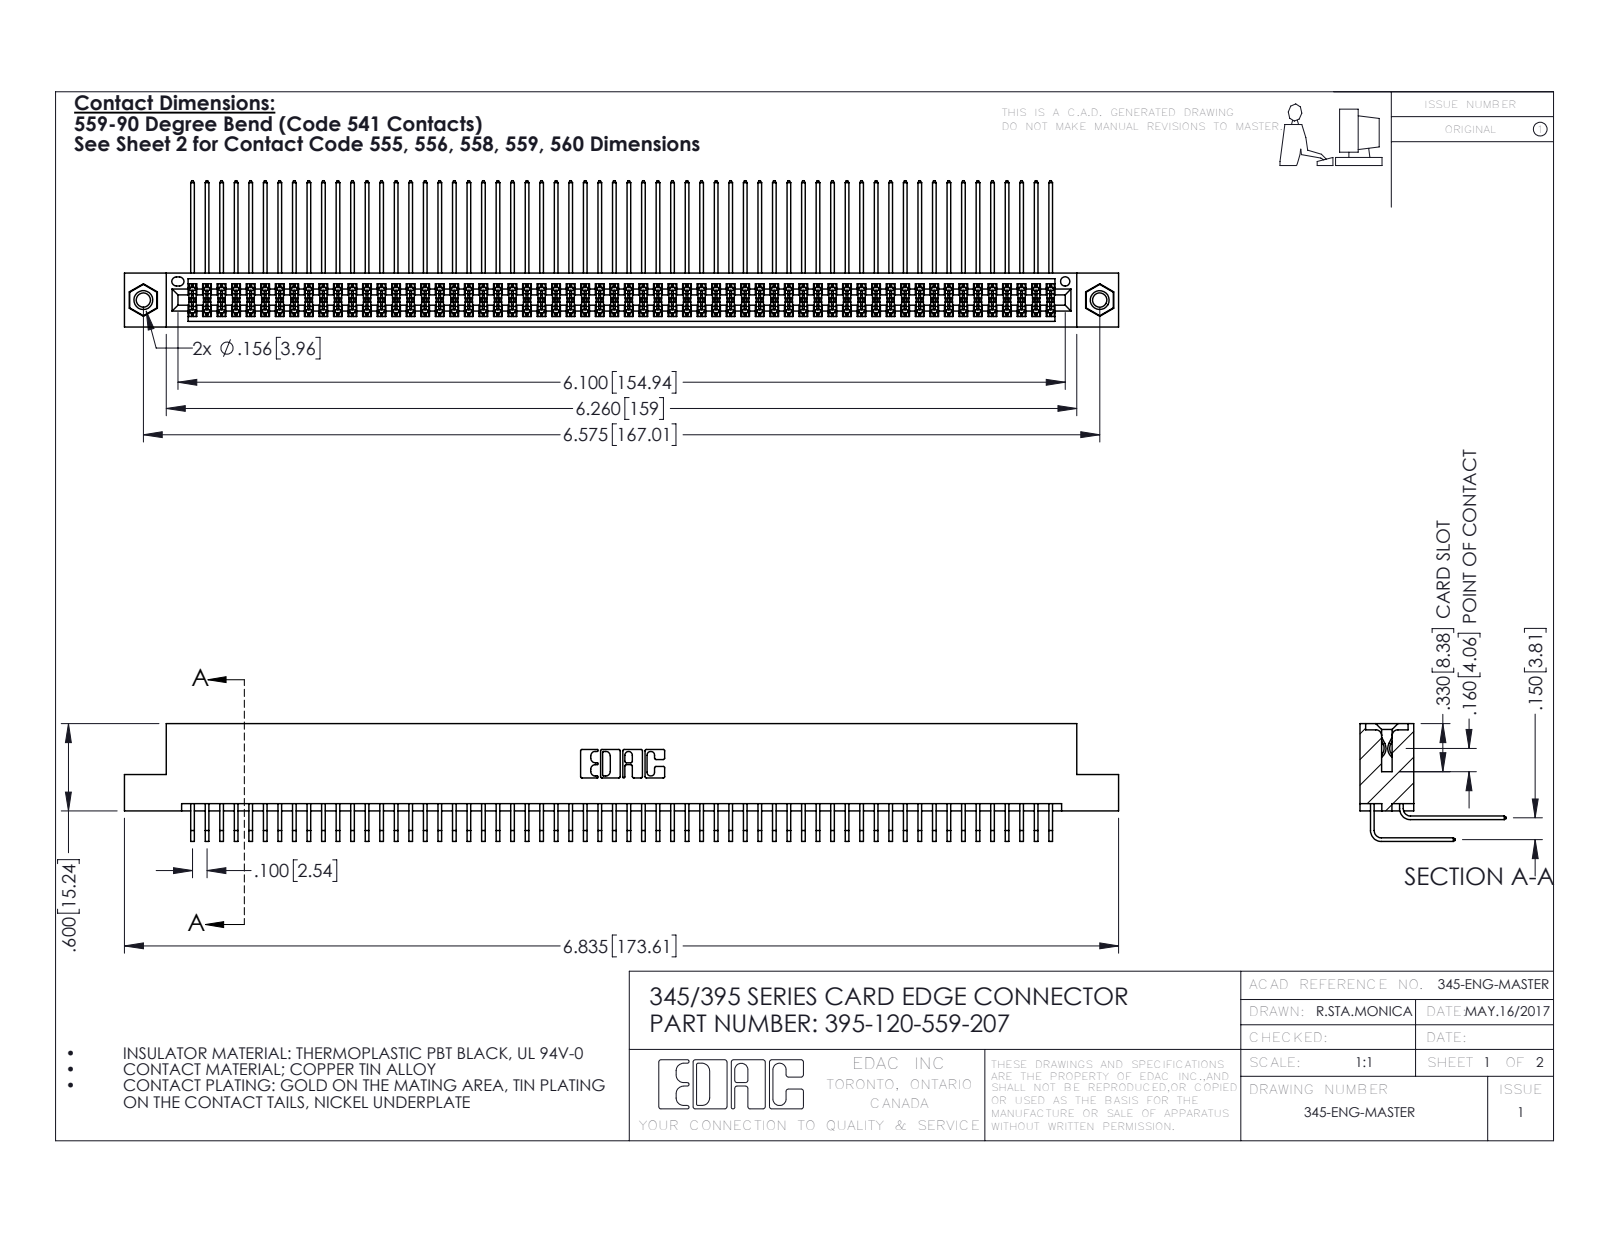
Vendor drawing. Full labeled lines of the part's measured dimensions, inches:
Part name (STEP PRODUCT): 345 Part_Flush Mounting Lugs - 0.156 Dia-TI; 345-292-001_559 Tail - 2; 345-292-001_558 559 Tail - 1; 345-250-001_345-250-005-103 (+1 more)
STEP written by: SolidWorks 2016 (CONFIG_CONTROL_DESIGN)
Units: inches
Bodies: 123 solids, 6426 faces (4312 planar, 2098 cylindrical, 16 other)
Overall size (bounding box): 6.835 × 1.005 × 0.809
Volume: 1.081 in³ · Surface area: 46.21 in²
Round holes (diameter × count): ⌀0.098 ×2, ⌀0.125 ×2, ⌀0.156 ×2, ⌀0.064 ×1
Round bosses / shafts (diameter × count): ⌀0.155 ×2
Partial cylindrical surfaces — rounded edges, fillets, slot ends (radius × count): R0.006 ×181, R0.01 ×22, R0.007 ×6, R0.031 ×6, R0.026 ×3, R0.014 ×2, R0.019 ×2, R0.022 ×2
Main face-to-face distances: 0.072, 0.298, 0.2, 0.37, 0.098, 0.272, 0.025, 0.225, 0.175, 0.15
Hole centre spacings: 0.27, 6.339, 6.575
